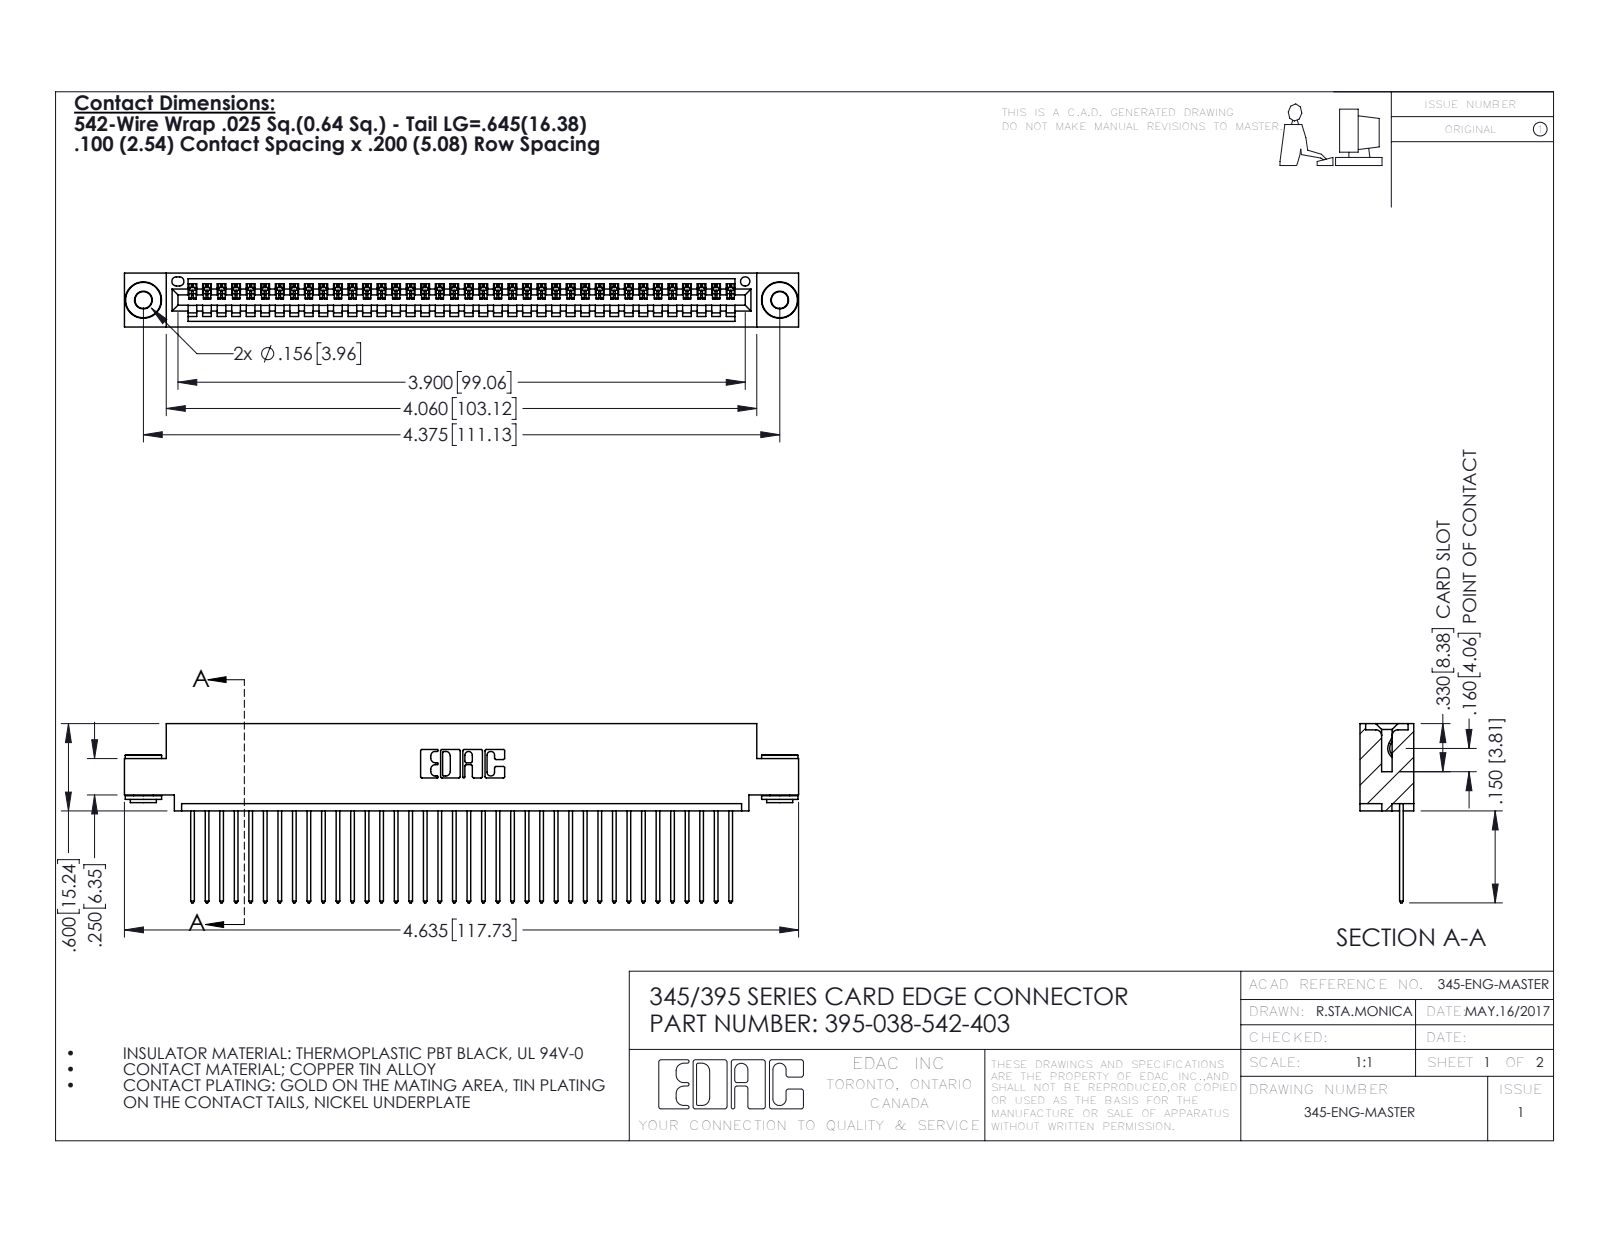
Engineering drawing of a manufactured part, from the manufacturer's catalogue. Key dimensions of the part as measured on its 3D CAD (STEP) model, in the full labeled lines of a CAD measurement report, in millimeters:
Part name (STEP PRODUCT): 395-038-542-403; 345-250-002_345-250-002-102; 345-292-001_345-293-142; 345 Part_0.110 Offset - 0.156 Dia-TH
STEP written by: SolidWorks 2016 (CONFIG_CONTROL_DESIGN)
Units: millimetres
Bodies: 41 solids, 2372 faces (1614 planar, 750 cylindrical, 8 other)
Overall size (bounding box): 117.7 × 31.3 × 9.4
Volume: 11 200 mm³ · Surface area: 15 630 mm²
Round holes (diameter × count): ⌀2.9 ×2, ⌀4 ×2, ⌀1.6 ×1
Round bosses / shafts (diameter × count): ⌀6.4 ×2, ⌀4.6 ×2, ⌀3.5 ×2
Partial cylindrical surfaces — rounded edges, fillets, slot ends (radius × count): R0.2 ×76, R0.3 ×76, R0.3 ×22, R0.2 ×6, R0.8 ×6, R0.7 ×3, R0.8 ×2, R1 ×2
Main face-to-face distances: 1.8, 7.6, 0.6, 9.4, 2.5, 6.9, 5.1, 5.7, 3.8, 1.8
Hole centre spacings: 6.9, 105.1, 111.1
